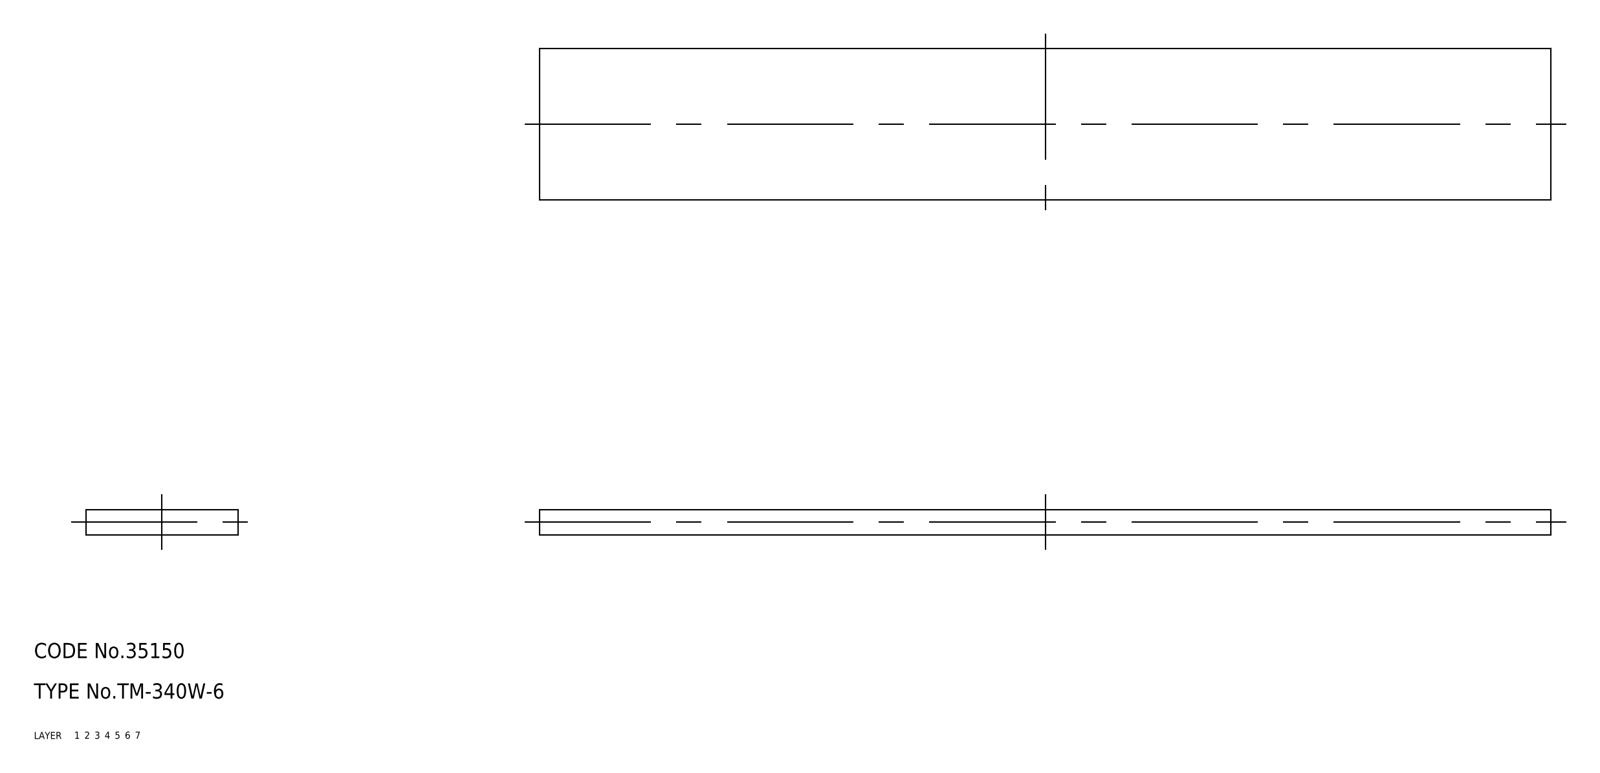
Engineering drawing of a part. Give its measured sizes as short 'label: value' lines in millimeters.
name: rubber foam; TM_340W_6
written by: SolidWorks 2015 (AUTOMOTIVE_DESIGN)
unit: mm
bodies: 1 solid, 6 faces (6 planar, 0 cylindrical, 0 other)
size: 200 × 30 × 5
volume: 30 000 mm³; area: 14 300 mm²
face distances: 5, 30, 200
